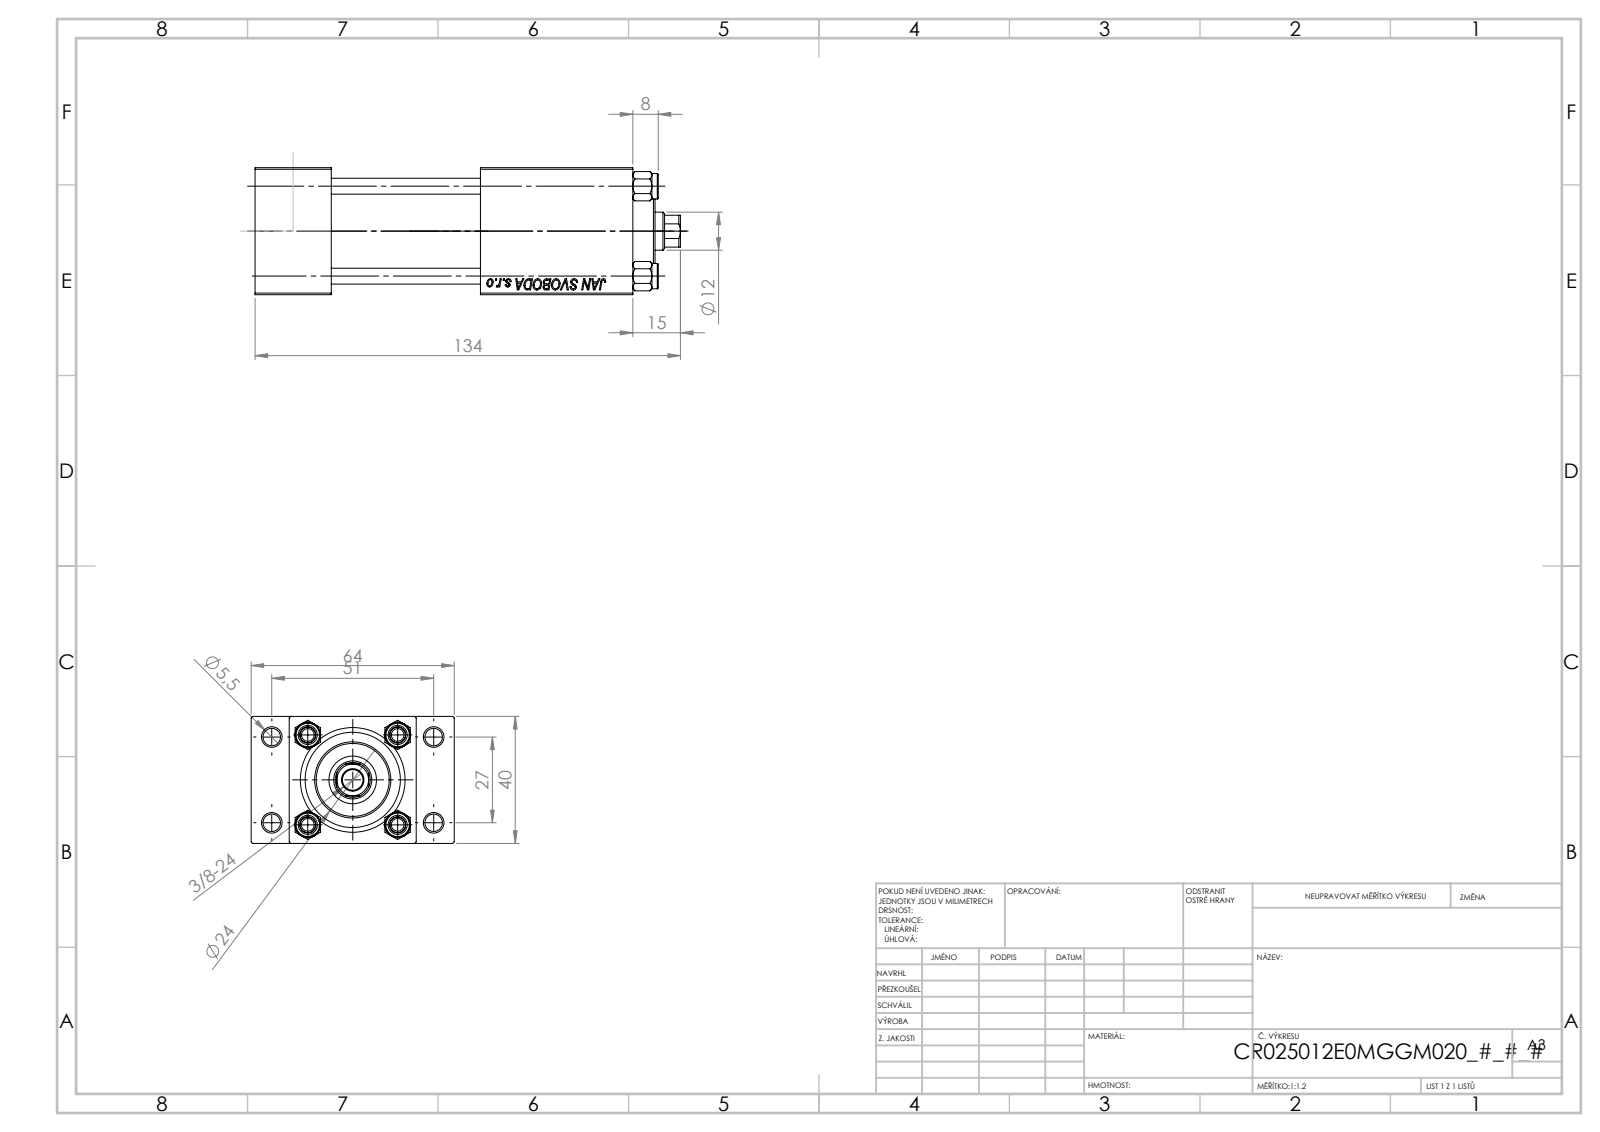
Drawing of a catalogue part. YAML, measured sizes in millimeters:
part_name: "V215CR_VCP_E; V215CR_E_Body; V215_VC_A; V215CR_TYCINKA_E (+1 more)"
step_written_by: "SolidWorks 2019 (CONFIG_CONTROL_DESIGN)"
units: millimeters
bodies: {solids: 11, faces: 1136, planar: 497, cylindrical: 87, other: 552}
overall_size: [134, 64, 40]
volume: 163915
surface_area: 62105
round_holes:
  - {diameter: 5, count: 4}
  - {diameter: 5.5, count: 4}
  - {diameter: 20, count: 3}
  - {diameter: 7, count: 2}
  - {diameter: 13.16, count: 2}
  - {diameter: 6.5, count: 1}
  - {diameter: 12, count: 1}
  - {diameter: 15, count: 1}
  - {diameter: 25, count: 1}
  - {diameter: 30, count: 1}
round_bosses_or_shafts:
  - {diameter: 8, count: 4}
  - {diameter: 31, count: 1}
  - {diameter: 24, count: 1}
partial_cylinders:
  - {radius: 5.5, count: 1}
face_to_face_distances: [40, 24, 12, 52, 119, 95, 90.3, 66.3, 28.7, 64]
hole_center_spacings: [11.37, 20.01, 28.3, 28.85, 29.89, 39.66, 48.34, 27]
